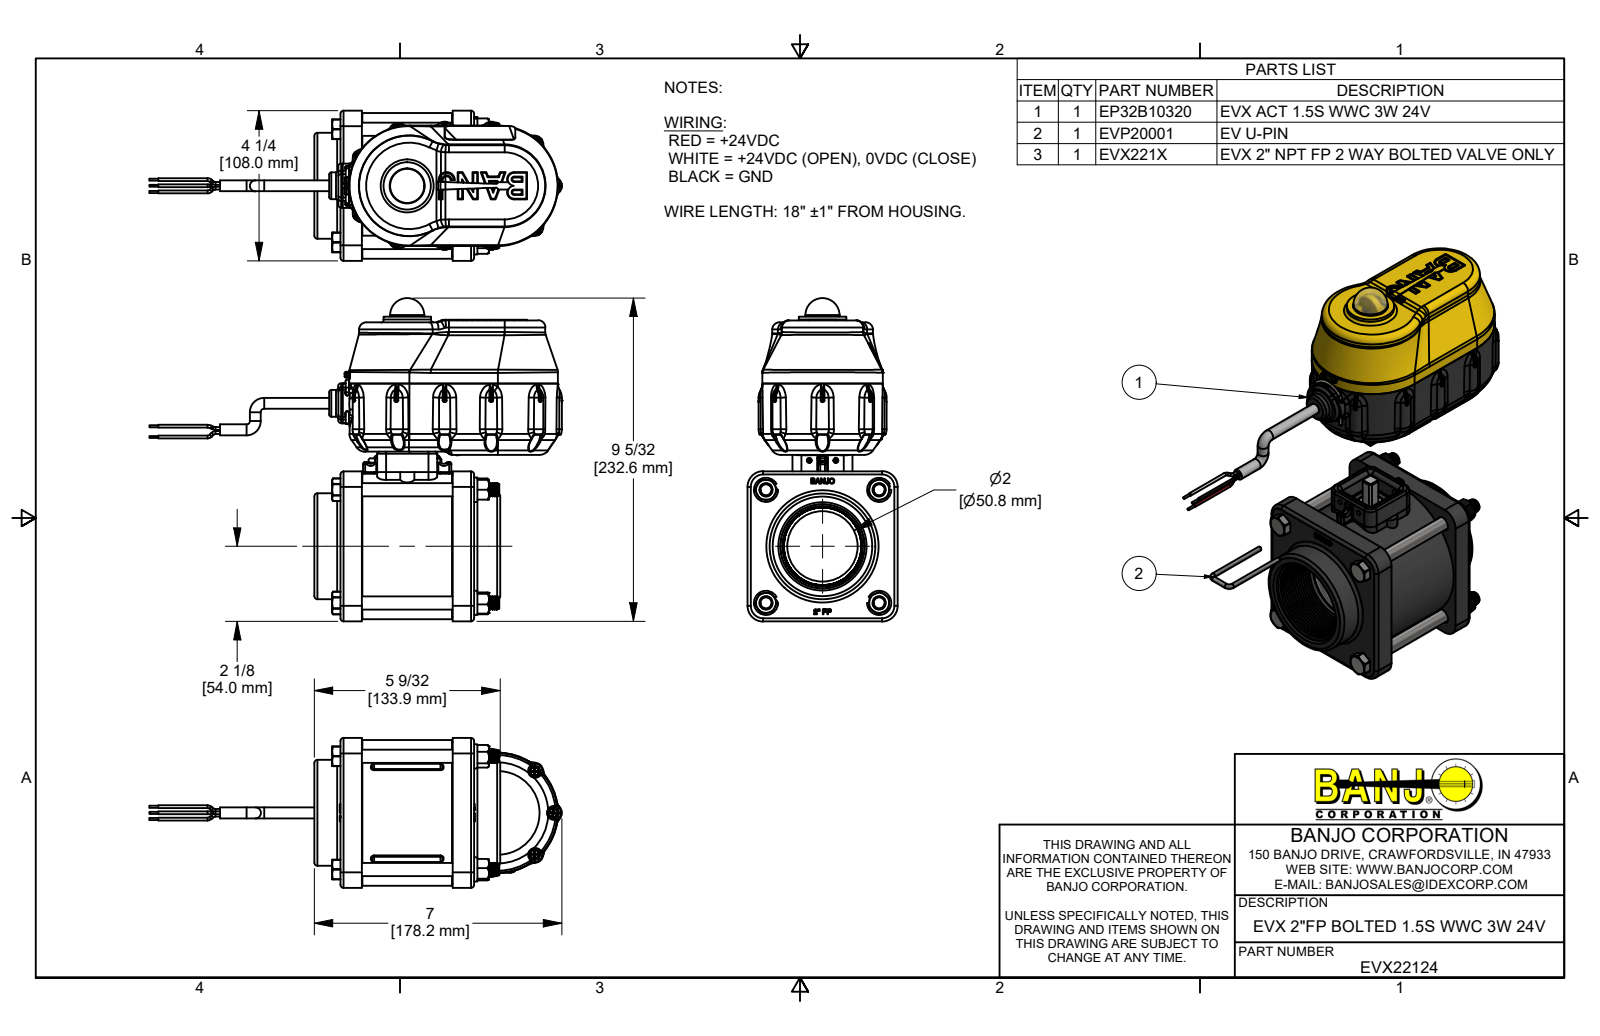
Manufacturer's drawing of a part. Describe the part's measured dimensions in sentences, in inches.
The part is named "EVX22124; EP32B10320; B61905PPHS; B632038PM (+8 more)". Its 3-D file was written by "Autodesk Inventor 2019 (AUTOMOTIVE_DESIGN)". It is 96 solids with 11339 faces: 2958 planar, 3327 cylindrical and 5054 other. Overall it measures 11.685 by 9.157 by 4.25 inches. Its volume is 70.85 cubic inches and its surface area 749.7 square inches. Round holes: 11 of diameter 0.095, 11 of diameter 0.15, 7 of diameter 0.08, 4 of diameter 0.107, 4 of diameter 0.126, 4 of diameter 0.135, 4 of diameter 0.136, 4 of diameter 0.148, 4 of diameter 0.15, 4 of diameter 0.17, 4 of diameter 0.307, 4 of diameter 0.385. Round bosses or shafts: 60 of diameter 0.324, 17 of diameter 0.25, 15 of diameter 0.08, 11 of diameter 0.14, 11 of diameter 0.108, 11 of diameter 0.085, 6 of diameter 0.058, 5 of diameter 0.375. Partial cylindrical surfaces (rounded edges, fillets, slot ends): 180 of radius 0.013, 145 of radius 0.04, 84 of radius 0.01, 74 of radius 0.02, 53 of radius 0.005, 38 of radius 0.03, 28 of radius 0.08, 24 of radius 0.06. The main face-to-face distances are 0.1, 2.565, 0.61, 3.18, 3.79, 2.485, 0.695, 3.095, 0.085, 0.211. The hole center spacings are 1.662, 2.265, 2.458, 2.656, 2.715, 3.204, 4.214, 4.49.
